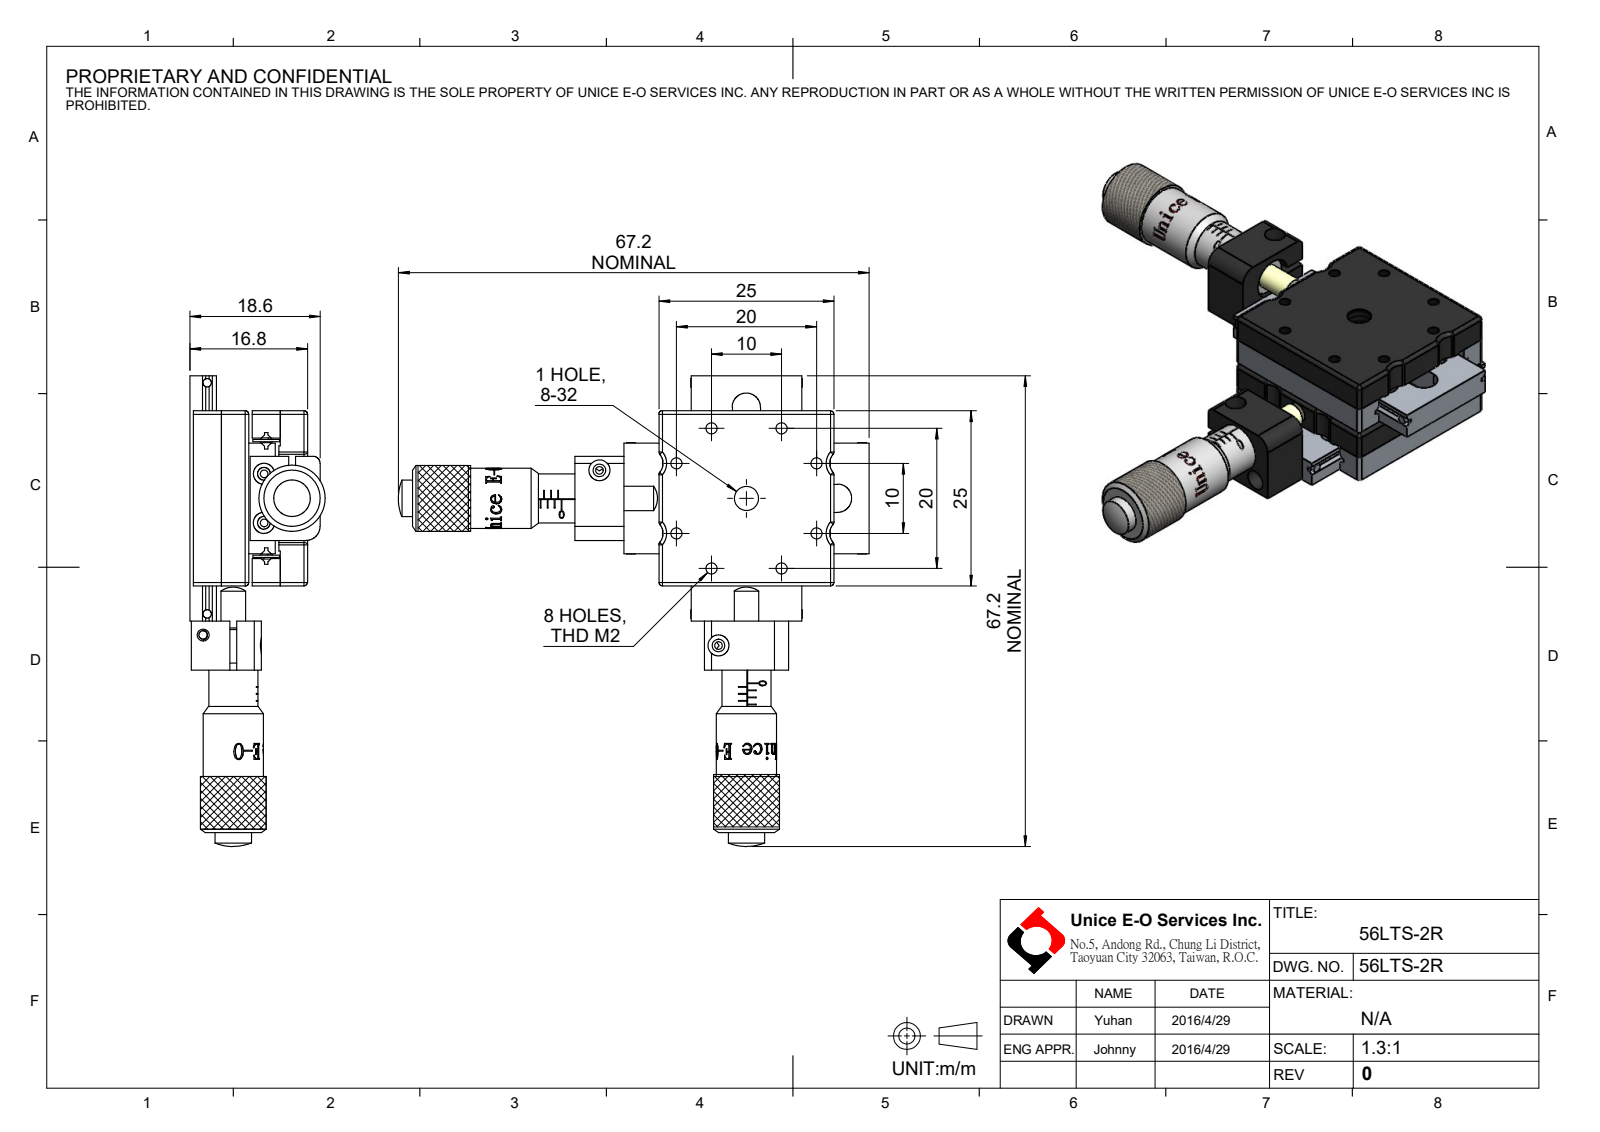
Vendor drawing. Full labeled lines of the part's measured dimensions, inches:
Part name (STEP PRODUCT): 56LTS-2R
STEP written by: SolidWorks 2016 (CONFIG_CONTROL_DESIGN)
Units: inches
Bodies: 42 solids, 1664 faces (666 planar, 622 cylindrical, 376 other)
Overall size (bounding box): 2.646 × 2.646 × 0.76
Volume: 0.817 in³ · Surface area: 24.97 in²
Round holes (diameter × count): ⌀0.043 ×20, ⌀0.071 ×18, ⌀0.122 ×12, ⌀0.047 ×8, ⌀0.063 ×8, ⌀0.094 ×8, ⌀0.118 ×8, ⌀0.157 ×8, ⌀0.067 ×2, ⌀0.098 ×2, ⌀0.102 ×2, ⌀0.138 ×2
Round bosses / shafts (diameter × count): ⌀0.059 ×21, ⌀0.37 ×2, ⌀0.339 ×2, ⌀0.276 ×2, ⌀0.252 ×2, ⌀0.224 ×2, ⌀0.205 ×2, ⌀0.047 ×2
Partial cylindrical surfaces — rounded edges, fillets, slot ends (radius × count): R0.02 ×28, R0.03 ×14, R0.079 ×14, R0.039 ×2, R0.169 ×2
Main face-to-face distances: 0.331, 0.181, 0.15, 0.028, 0.154, 0.02, 0.169, 0.161, 0.177, 0.35
Hole centre spacings: 0.159, 0.198, 0.222, 0.354, 0.42, 0.44, 0.45, 0.546
